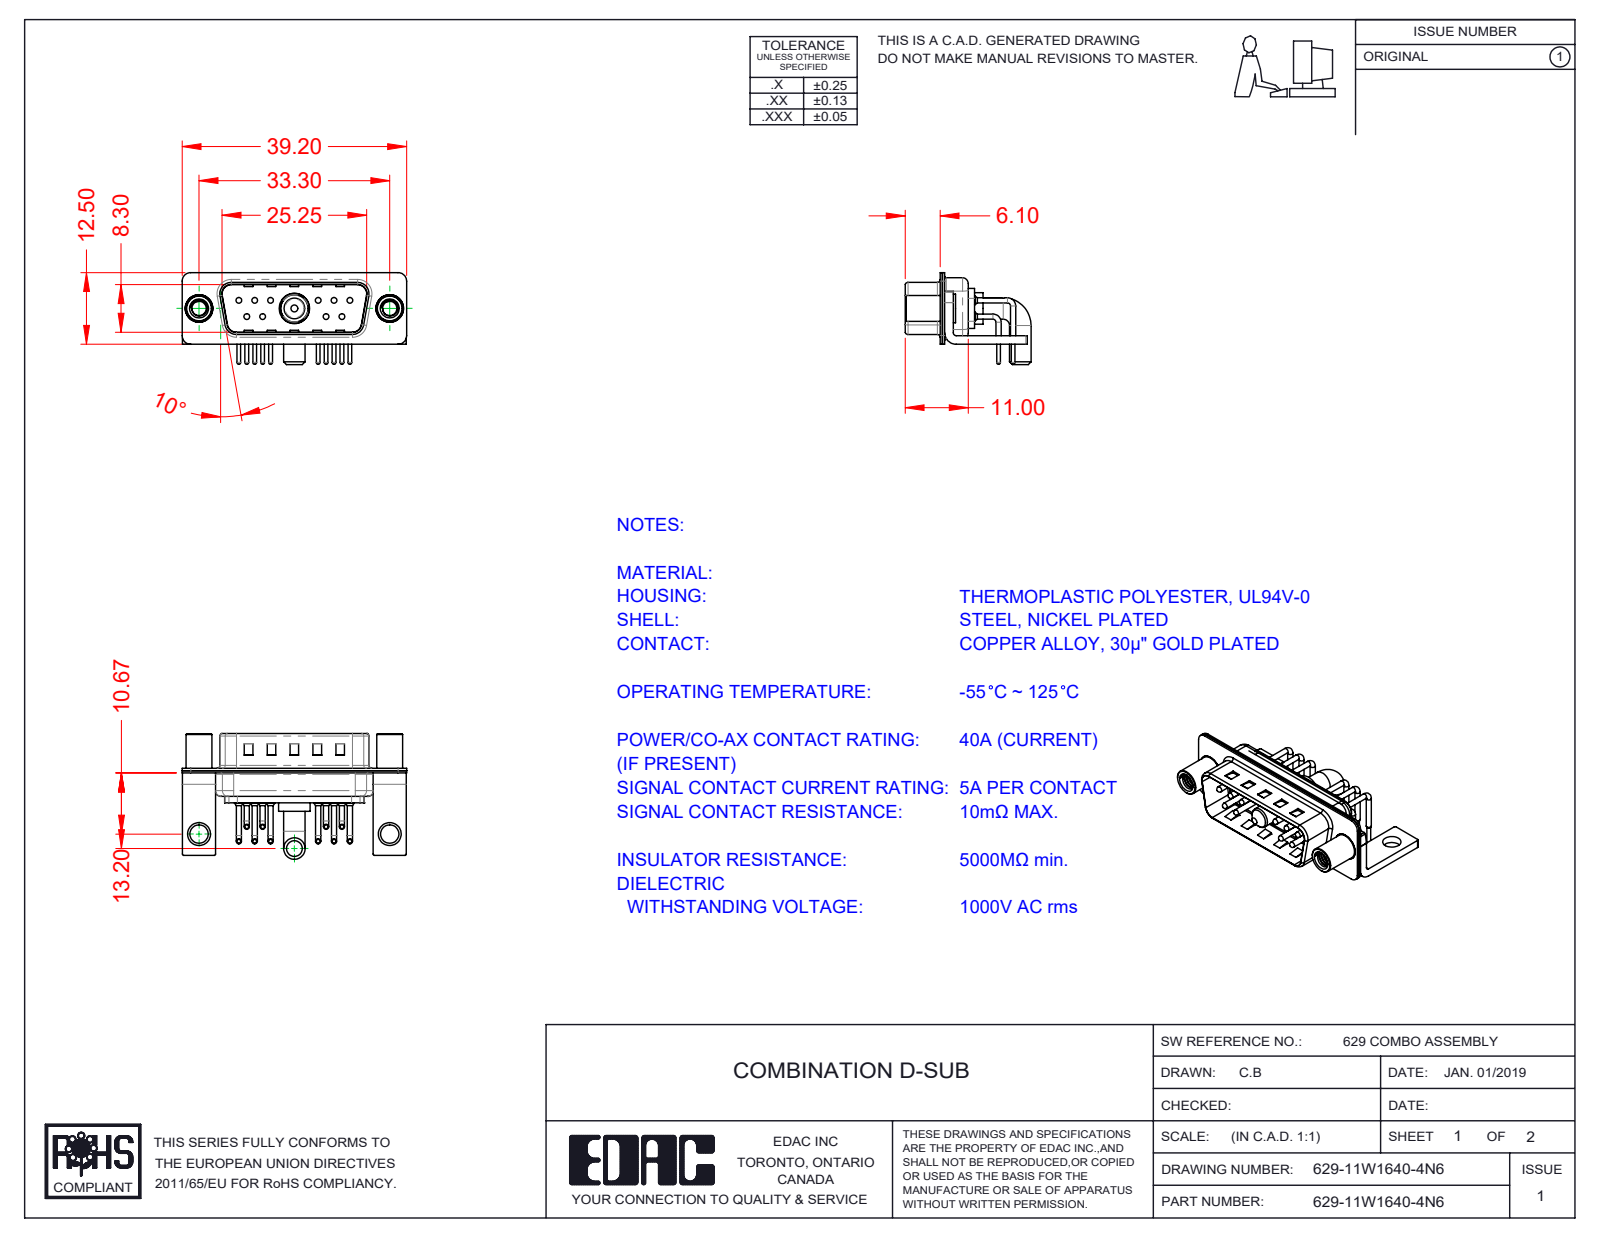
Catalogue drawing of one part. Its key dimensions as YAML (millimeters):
part_name: "629Combo Housing_11W1; 629Combo Contact Row 1; 629Combo Shell Front_15 Contacts; 629Combo Stabilizer Bracket (+5 more)"
step_written_by: "SolidWorks 2020 (CONFIG_CONTROL_DESIGN)"
units: millimeters
bodies: {solids: 19, faces: 1594, planar: 820, cylindrical: 590, other: 184}
overall_size: [39.2, 21.98, 16.05]
volume: 2520
surface_area: 6202
round_holes:
  - {diameter: 0.75, count: 10}
  - {diameter: 1.6, count: 10}
  - {diameter: 2, count: 10}
  - {diameter: 2.5, count: 2}
  - {diameter: 3.2, count: 2}
  - {diameter: 4, count: 2}
  - {diameter: 4.8, count: 2}
  - {diameter: 4.85, count: 1}
  - {diameter: 5.3, count: 1}
round_bosses_or_shafts:
  - {diameter: 0.9, count: 20}
  - {diameter: 1.5, count: 10}
  - {diameter: 1, count: 10}
  - {diameter: 0.65, count: 10}
  - {diameter: 5, count: 2}
  - {diameter: 4.9, count: 2}
  - {diameter: 4.5, count: 2}
  - {diameter: 3.75, count: 2}
partial_cylinders:
  - {radius: 0.25, count: 16}
  - {radius: 1.5, count: 16}
  - {radius: 2, count: 13}
  - {radius: 1.01, count: 10}
  - {radius: 0.5, count: 9}
  - {radius: 1.6, count: 8}
  - {radius: 1, count: 7}
  - {radius: 0.6, count: 4}
face_to_face_distances: [0.4, 0.8, 1.5, 9.5, 9.1, 8.7, 9.9, 0.6, 1.9, 2.1]
hole_center_spacings: [3.16, 2.77, 13.85, 11.08, 16.62, 5.03, 5.04, 5.54]
